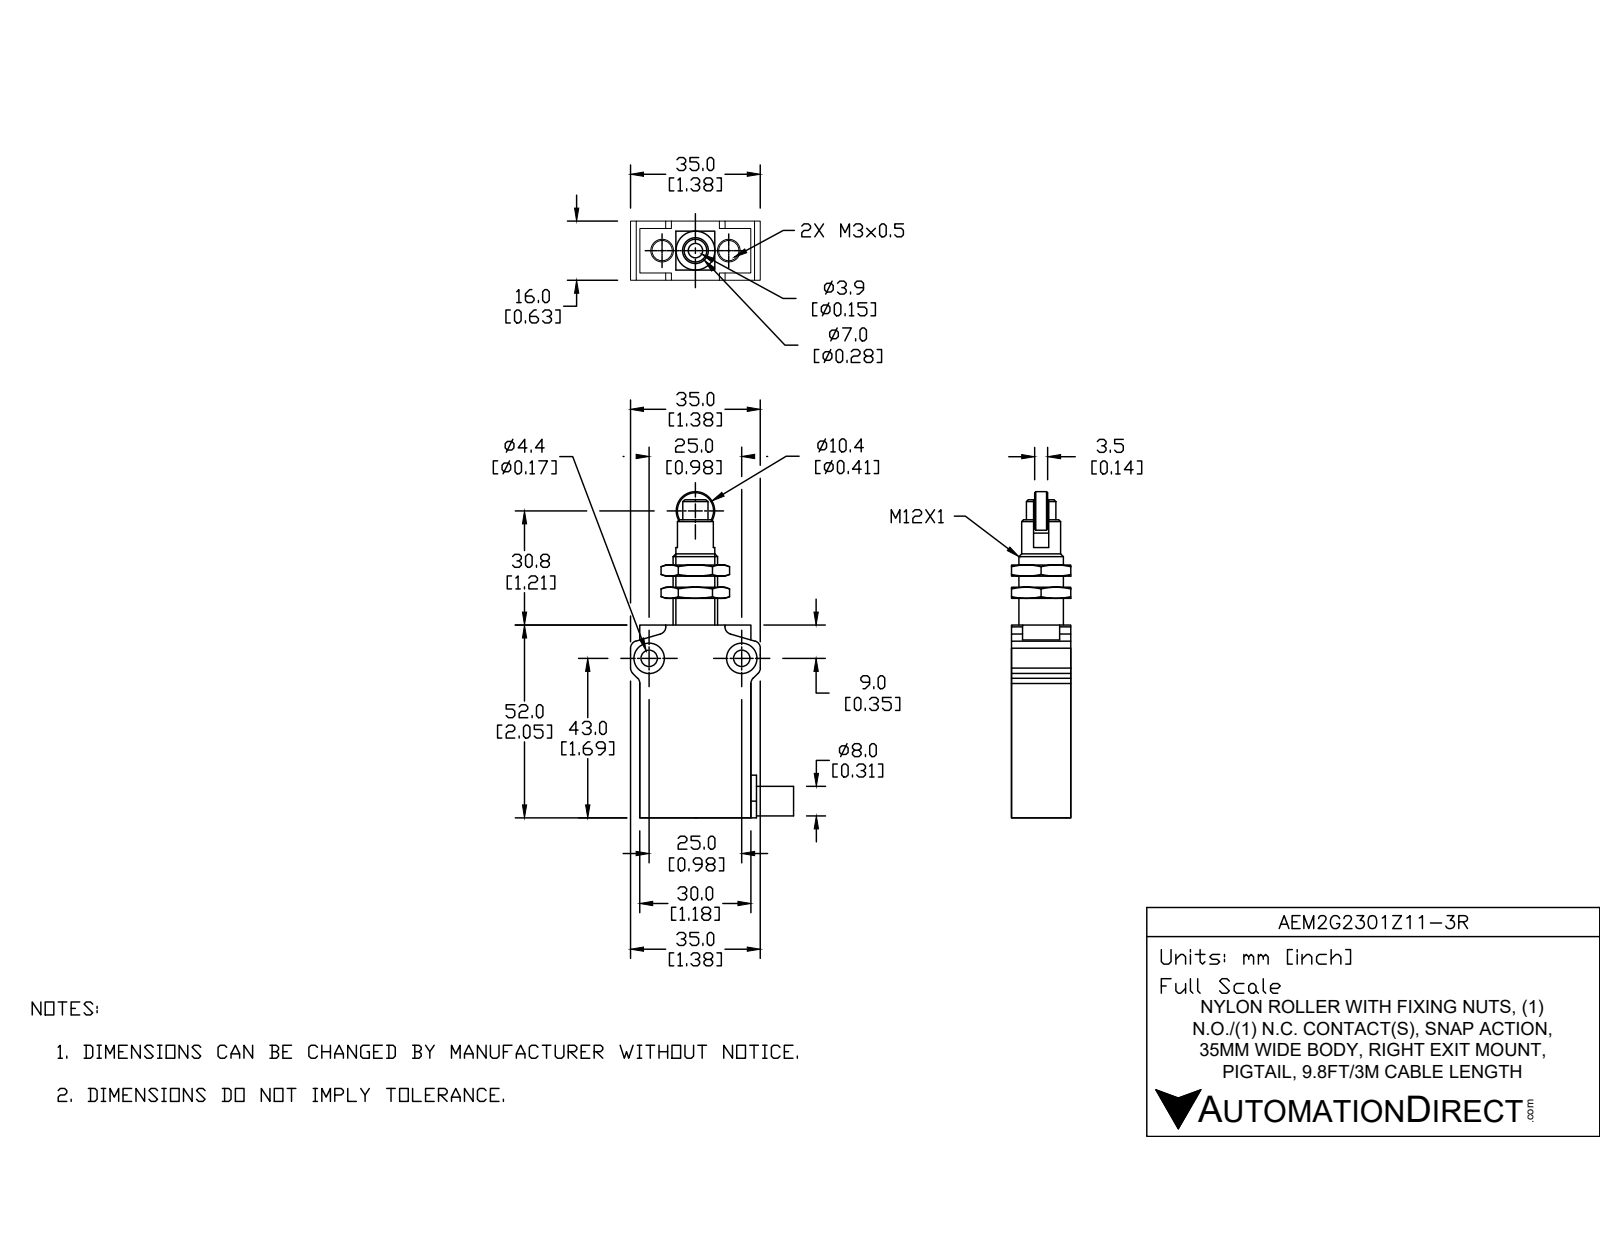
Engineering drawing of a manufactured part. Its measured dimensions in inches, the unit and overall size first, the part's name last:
Units: inches
Overall size (bounding box): 3.346 × 1.87 × 0.63
Round holes (diameter × count): ⌀0.118 ×2, ⌀0.173 ×2, ⌀0.323 ×2, ⌀0.317 ×1, ⌀0.472 ×1
Round bosses / shafts (diameter × count): ⌀0.413 ×1, ⌀0.409 ×1, ⌀0.323 ×1, ⌀0.313 ×1, ⌀0.22 ×1
Partial cylindrical surfaces — rounded edges, fillets, slot ends (radius × count): R0.079 ×8, R0.256 ×1
Main face-to-face distances: 0.63, 1.181, 0.472, 0.118, 0.236, 1.929, 1.74, 0.189, 0.354, 0.157
Hole centre spacings: 0.374, 0.748, 0.984
Volume: 1.658 in³ · Surface area: 17.53 in²
Bodies: 7 solids, 178 faces (79 planar, 56 cylindrical, 43 other)
Part name (STEP PRODUCT): AEM2G2301Z11-3R
STEP written by: SolidWorks 2017 (AUTOMOTIVE_DESIGN)
